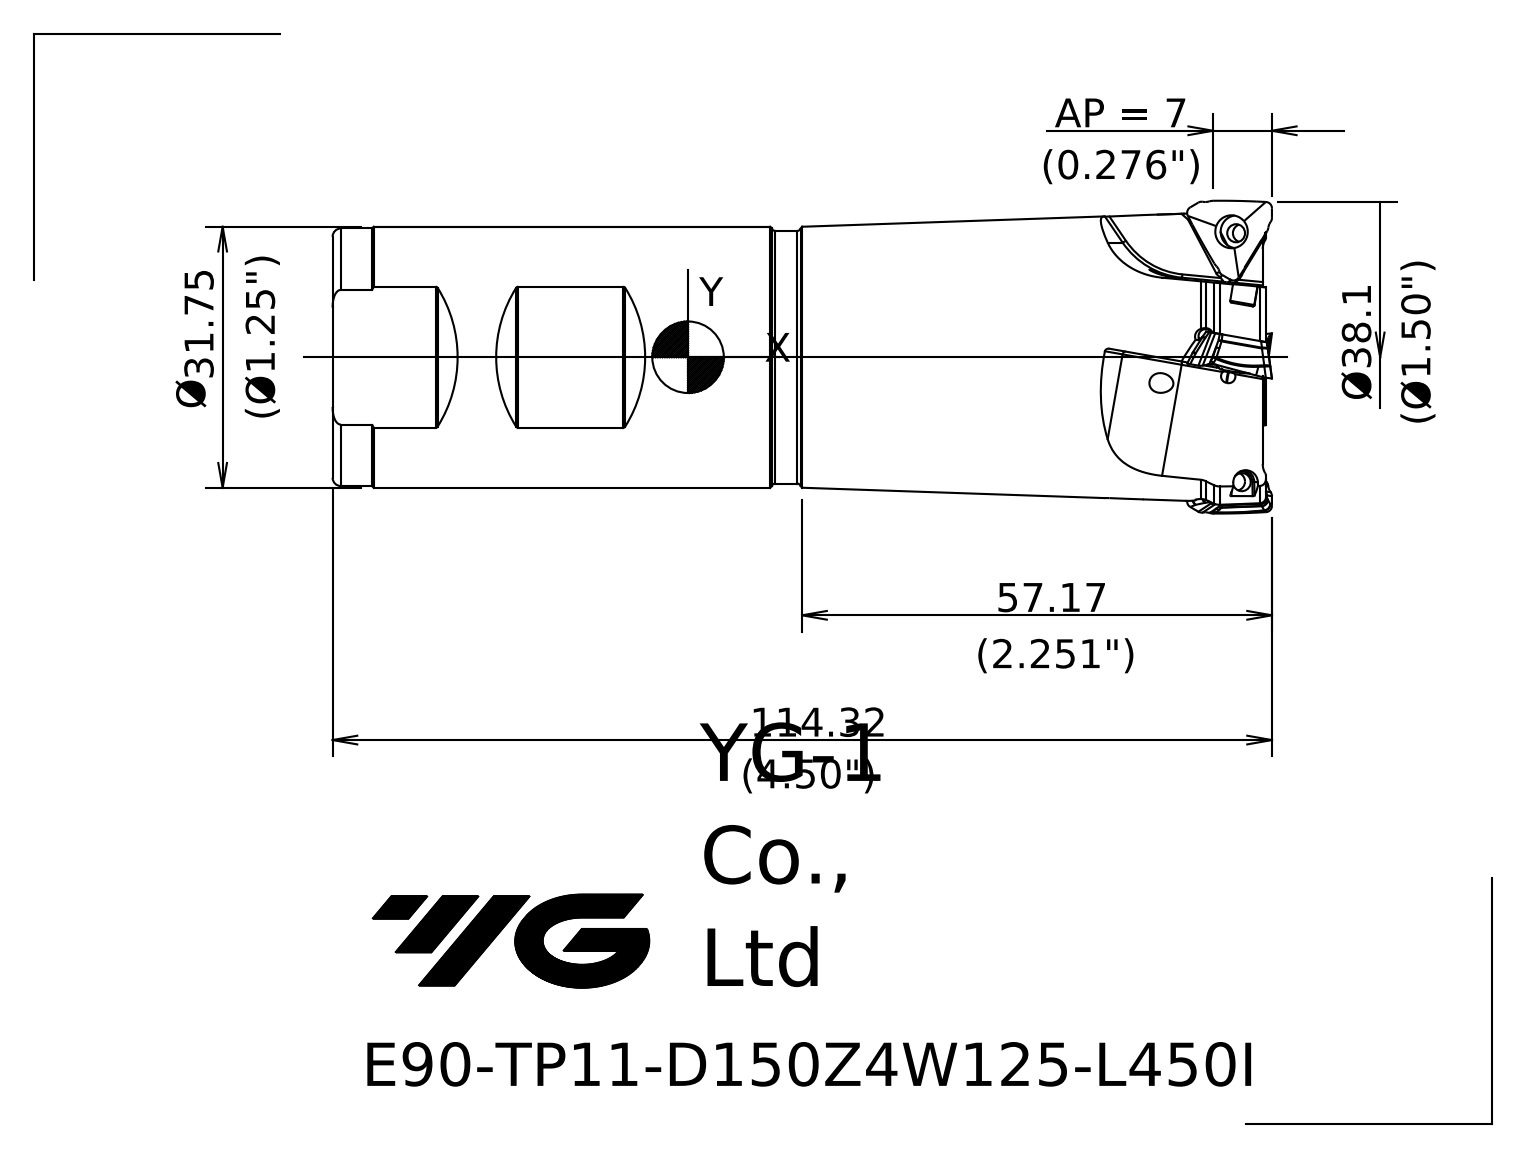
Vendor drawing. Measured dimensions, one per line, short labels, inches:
name: 10222DA0A397nvme
written by: SIEMENS PLM Software NX 10.0 (AP203_CONFIGURATION_CONTROLLED_3D_DESIGN_OF_MECHANICAL_PARTS_AND_ASSEMBLIES_MIM_LF)
unit: in
bodies: 1 solid, 58 faces (8 planar, 8 cylindrical, 42 other)
size: 4.501 × 1.504 × 1.504
volume: 5.485 in³; area: 29.08 in²
holes: 1× ⌀0.059, 1× ⌀0.315
bosses: 1× ⌀1.25, 1× ⌀1.234, 1× ⌀1.211
rounds: 3× R0.012
face distances: 4.457, 0.635, 0.016, 4.472
